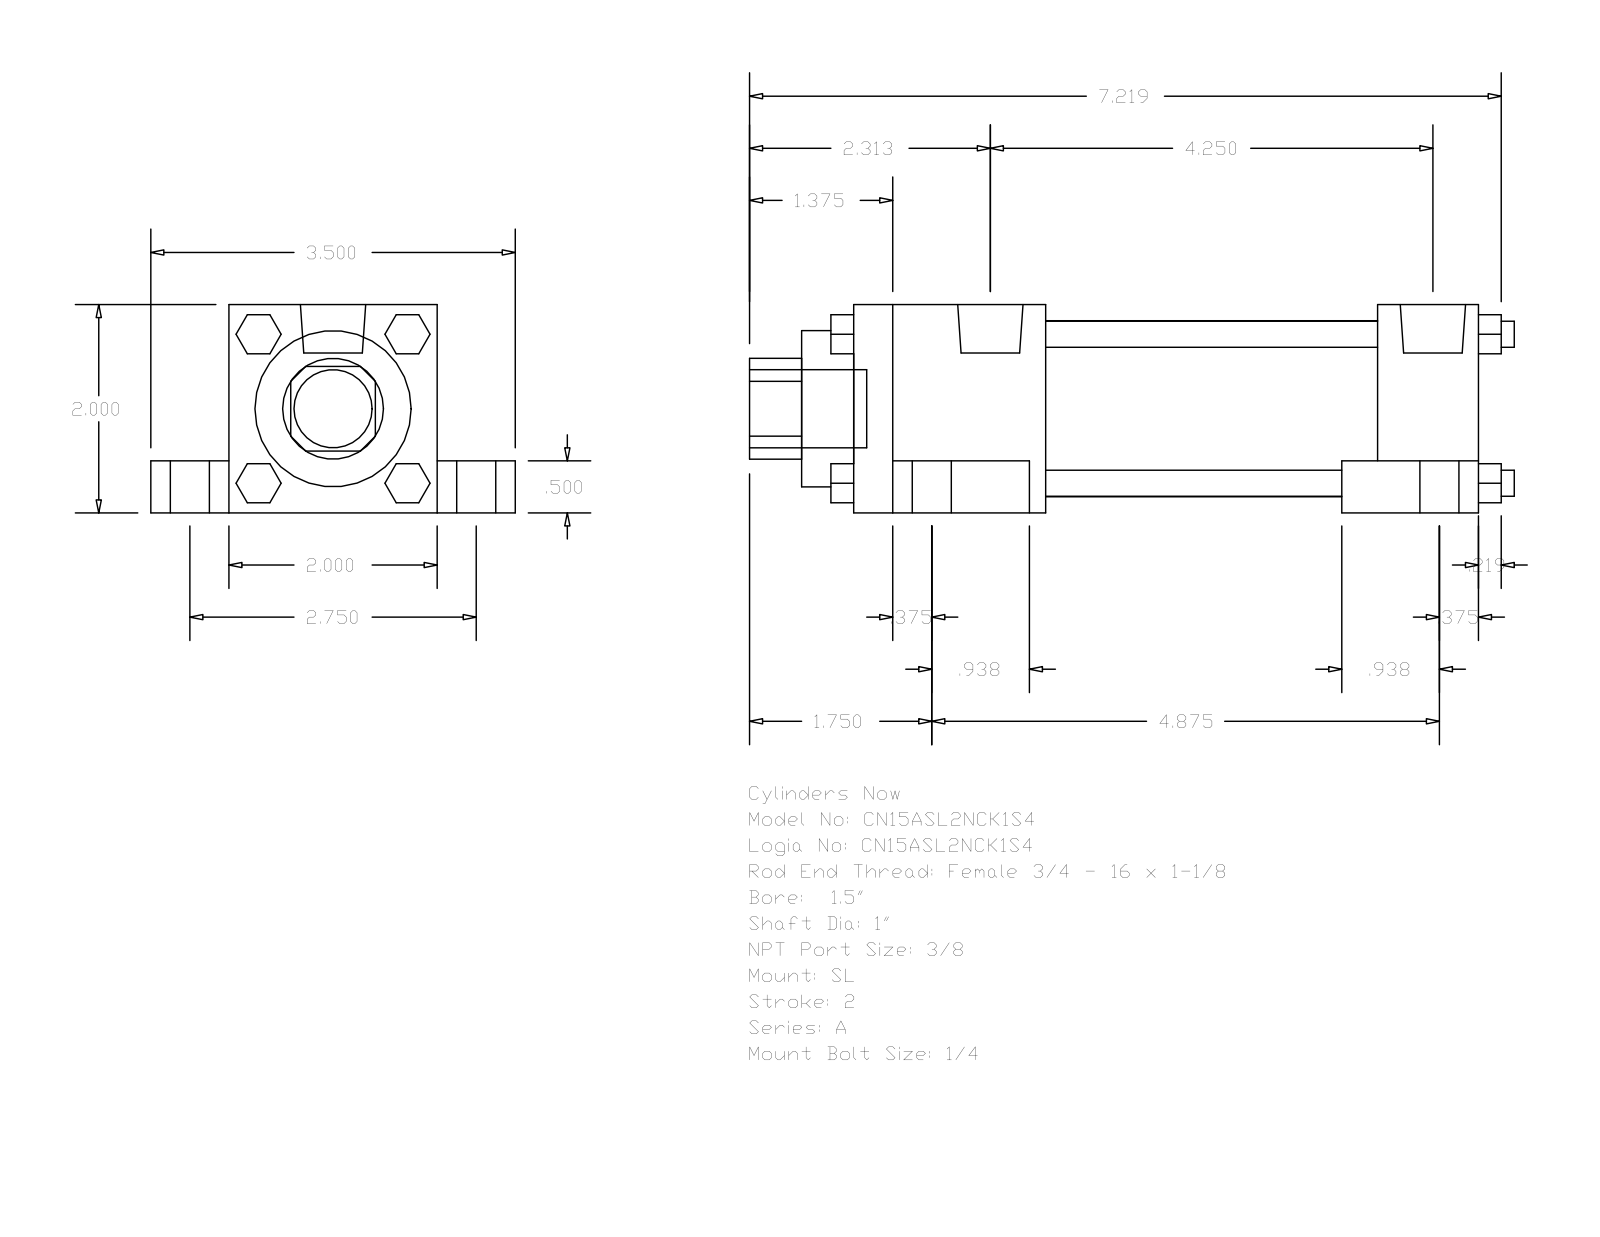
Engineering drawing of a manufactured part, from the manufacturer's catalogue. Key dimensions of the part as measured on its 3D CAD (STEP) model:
Part name (STEP PRODUCT): A_SL__0150_1
STEP written by: GSSL Pune (CONFIG_CONTROL_DESIGN)
Units: millimetres
Bodies: 0 solids, 148 faces (112 planar, 36 cylindrical, 0 other)
Overall size (bounding box): 186.53 × 88.9 × 50.8
Round holes (diameter × count): ⌀25.4 ×1, ⌀38.1 ×1, ⌀42.93 ×1
Round bosses / shafts (diameter × count): ⌀15.88 ×4, ⌀9.53 ×4, ⌀6.35 ×4, ⌀5.56 ×4, ⌀15.93 ×2, ⌀19.05 ×1
Partial cylindrical surfaces — rounded edges, fillets, slot ends (radius × count): R12.29 ×1
Main face-to-face distances: 50.8, 12.7, 38.1, 19.05, 69.85, 9.52, 152.4, 33.34, 127.79, 24.61
